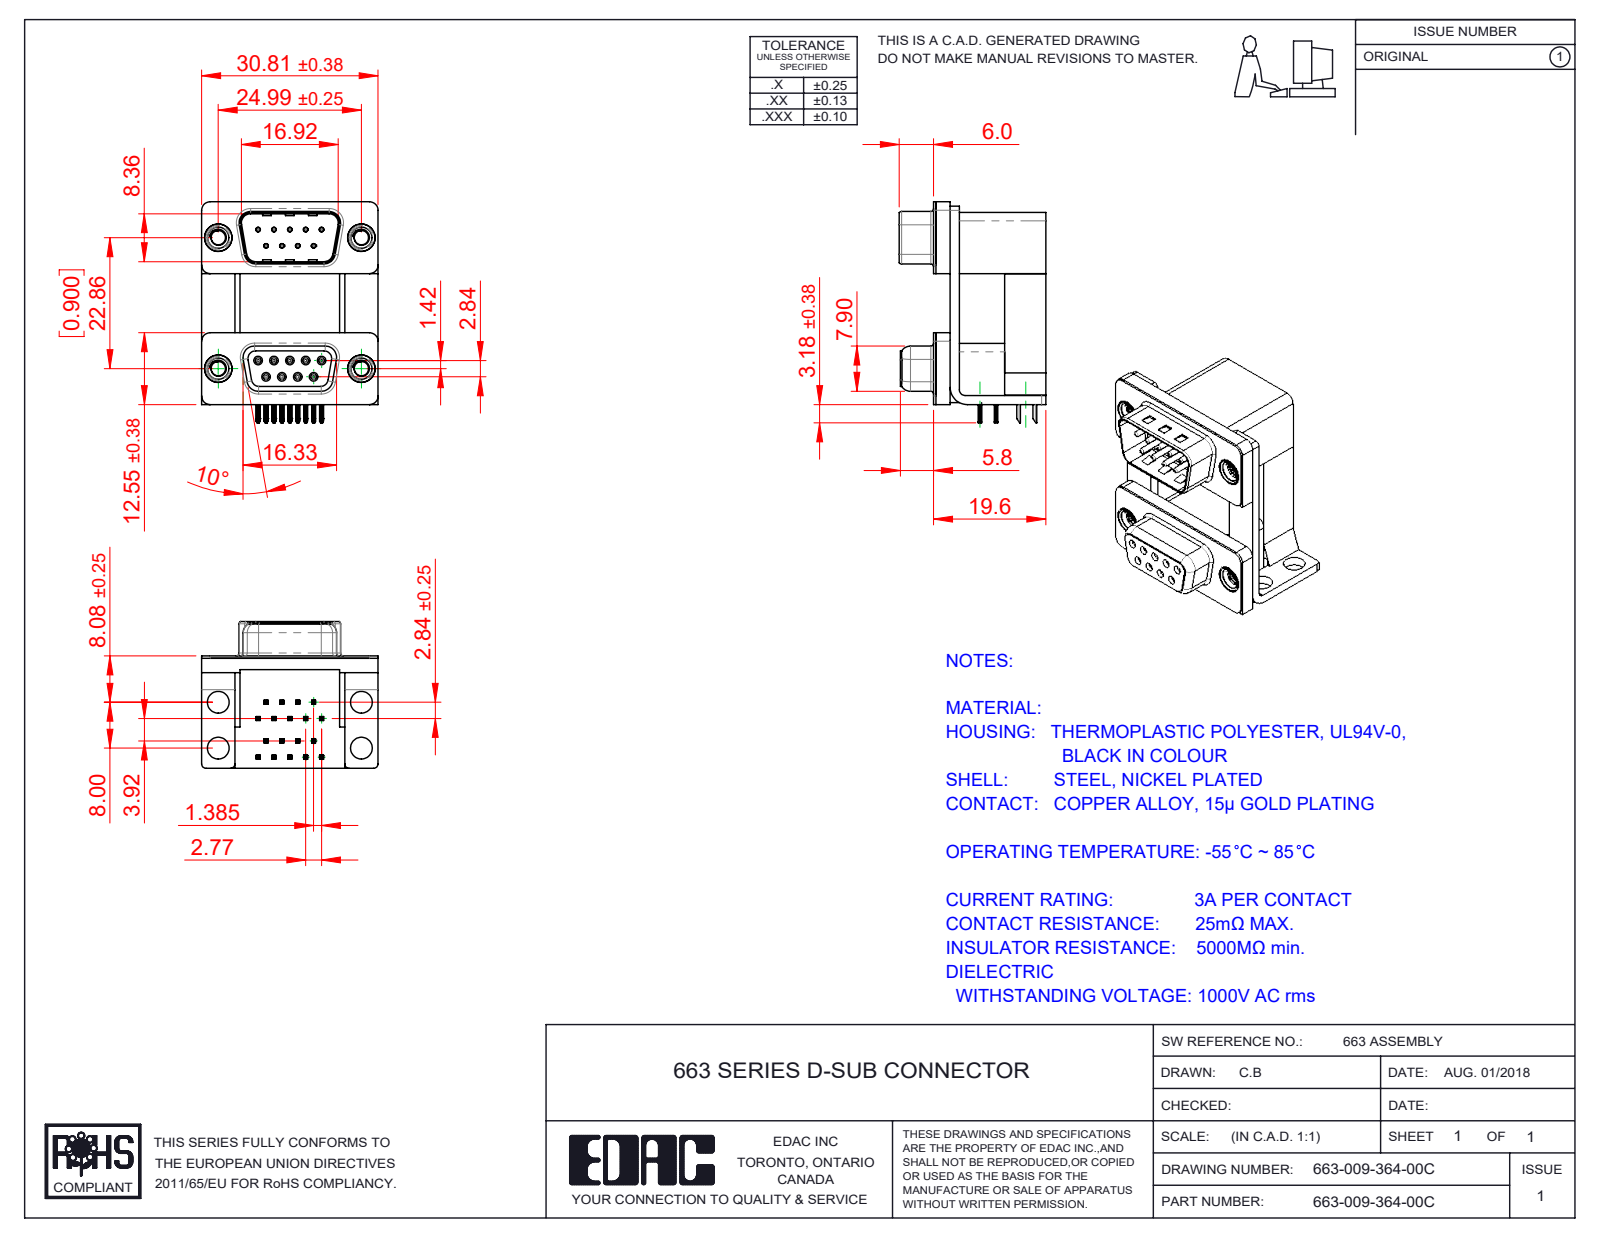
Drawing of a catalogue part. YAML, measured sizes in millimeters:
part_name: "663 Mounting Bracket_NoneH; 663 Contact Bottom Upper_H; 663 Housing Lower_09 Contacts; 663 Housing Spacer_09 Contacts H (+8 more)"
step_written_by: "SolidWorks 2020 (CONFIG_CONTROL_DESIGN)"
units: millimeters
bodies: {solids: 29, faces: 2533, planar: 1263, cylindrical: 703, other: 567}
overall_size: [38.59, 30.81, 25.6]
volume: 11324
surface_area: 12959
round_holes:
  - {diameter: 0.8, count: 18}
  - {diameter: 0.35, count: 9}
  - {diameter: 0.9, count: 9}
  - {diameter: 2.5, count: 4}
  - {diameter: 3.5, count: 4}
  - {diameter: 3.8, count: 4}
  - {diameter: 4, count: 4}
  - {diameter: 4.8, count: 4}
  - {diameter: 5, count: 4}
round_bosses_or_shafts:
  - {diameter: 1.2, count: 9}
  - {diameter: 0.75, count: 9}
  - {diameter: 4.9, count: 4}
  - {diameter: 4.75, count: 4}
  - {diameter: 3.9, count: 4}
partial_cylinders:
  - {radius: 0.1, count: 72}
  - {radius: 0.15, count: 36}
  - {radius: 0.25, count: 36}
  - {radius: 0.12, count: 18}
  - {radius: 0.35, count: 18}
  - {radius: 1.5, count: 15}
  - {radius: 0.5, count: 12}
  - {radius: 0.34, count: 9}
face_to_face_distances: [2.5, 0.4, 19.2, 16.7, 12, 7.2, 9.5, 1.6, 12.4, 22.86]
hole_center_spacings: [3.16, 2.77, 23.03, 22.86, 5.54, 23.52, 20.07, 25.74]
